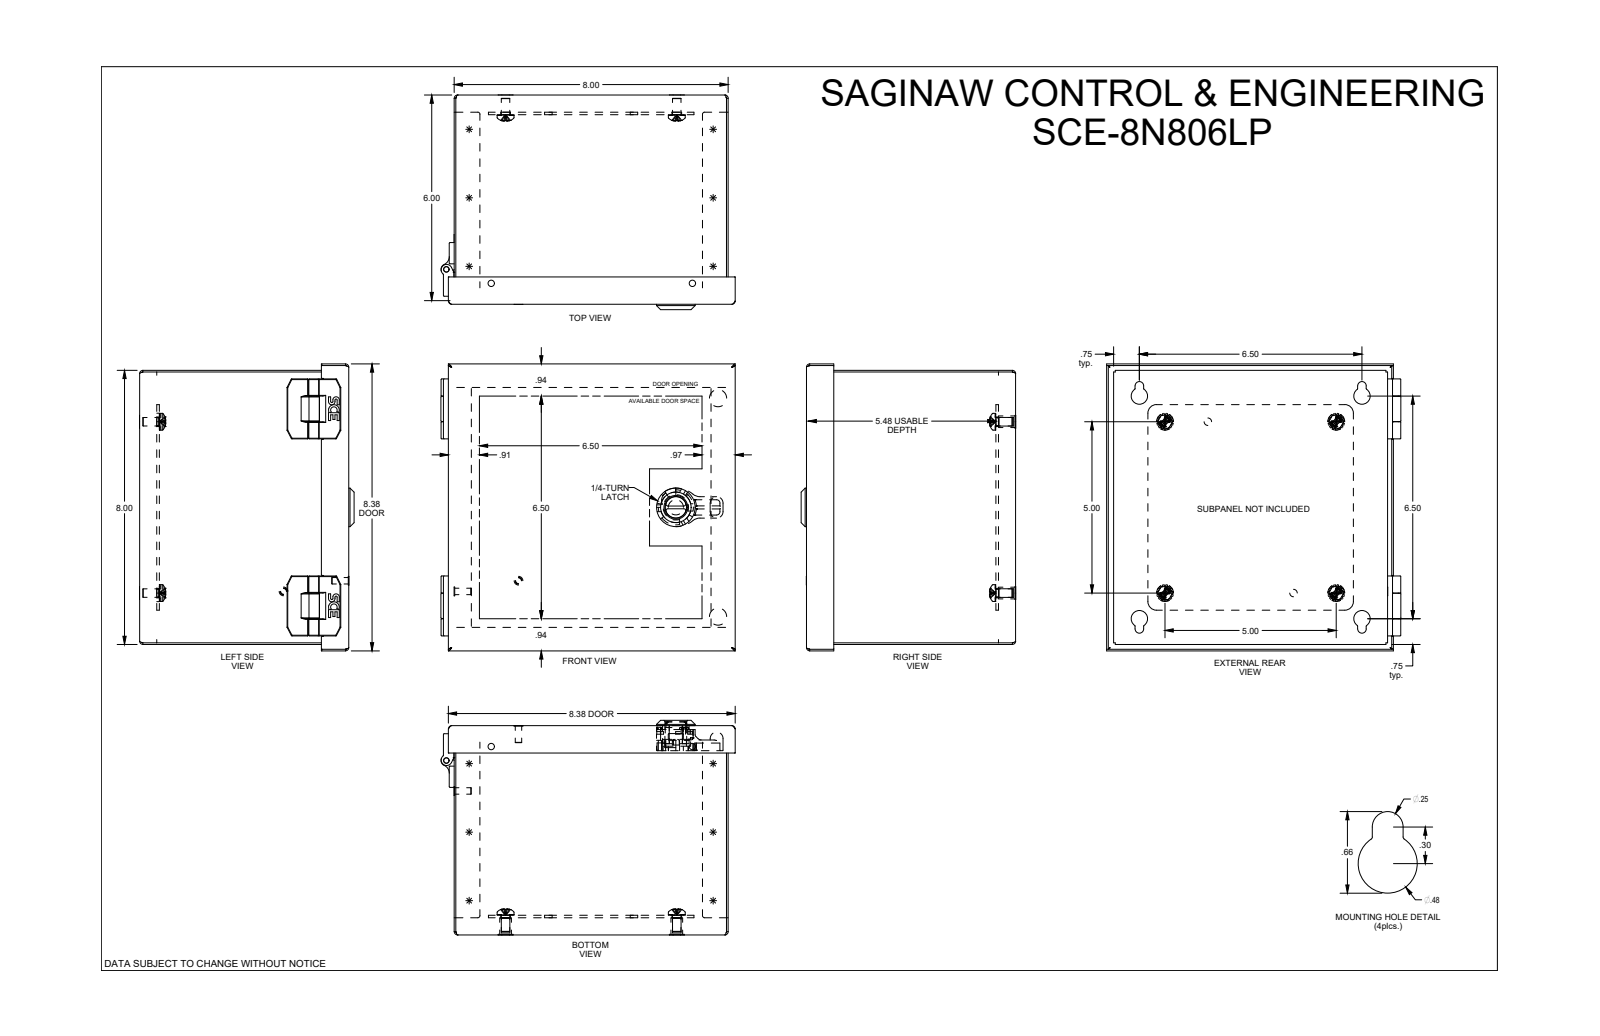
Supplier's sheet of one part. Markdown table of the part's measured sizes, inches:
| quantity | value |
| --- | --- |
| part name | SCE-8N806LP_REV1 |
| STEP written by | SolidWorks 2021 (AUTOMOTIVE_DESIGN) |
| units | inches |
| bodies | 23 solids, 746 faces (249 planar, 318 cylindrical, 179 other) |
| overall size | 8.593 × 8.375 × 6.263 |
| volume | 26.05 in³ |
| surface area | 834.1 in² |
| round holes (diameter × count) | 0.203 × 4, 0.25 × 4, 0.281 × 4, 0.343 × 4, 0.48 × 4, 0.218 × 2, 0.329 × 2, 0.158 × 1, 0.187 × 1, 0.193 × 1, 0.44 × 1, 0.635 × 1 |
| round bosses / shafts (diameter × count) | 0.376 × 4, 0.237 × 4, 0.16 × 4, 0.5 × 2, 0.323 × 2, 0.248 × 2, 1.125 × 1, 1.125 × 1 |
| partial cylindrical surfaces (radius × count) | 0.02 × 95, 0.06 × 25, 0.015 × 16, 0.01 × 13, 0.055 × 6, 0.25 × 6, 0.125 × 4, 0.05 × 2 |
| main face-to-face distances | 0.06, 7.94, 6.047, 7.88, 8, 5.987, 6.107, 0.548, 0.488, 5.499 |
| hole center spacings | 5.799, 1.061, 5, 6.5, 8.132, 1.25, 2.136, 2.5 |
